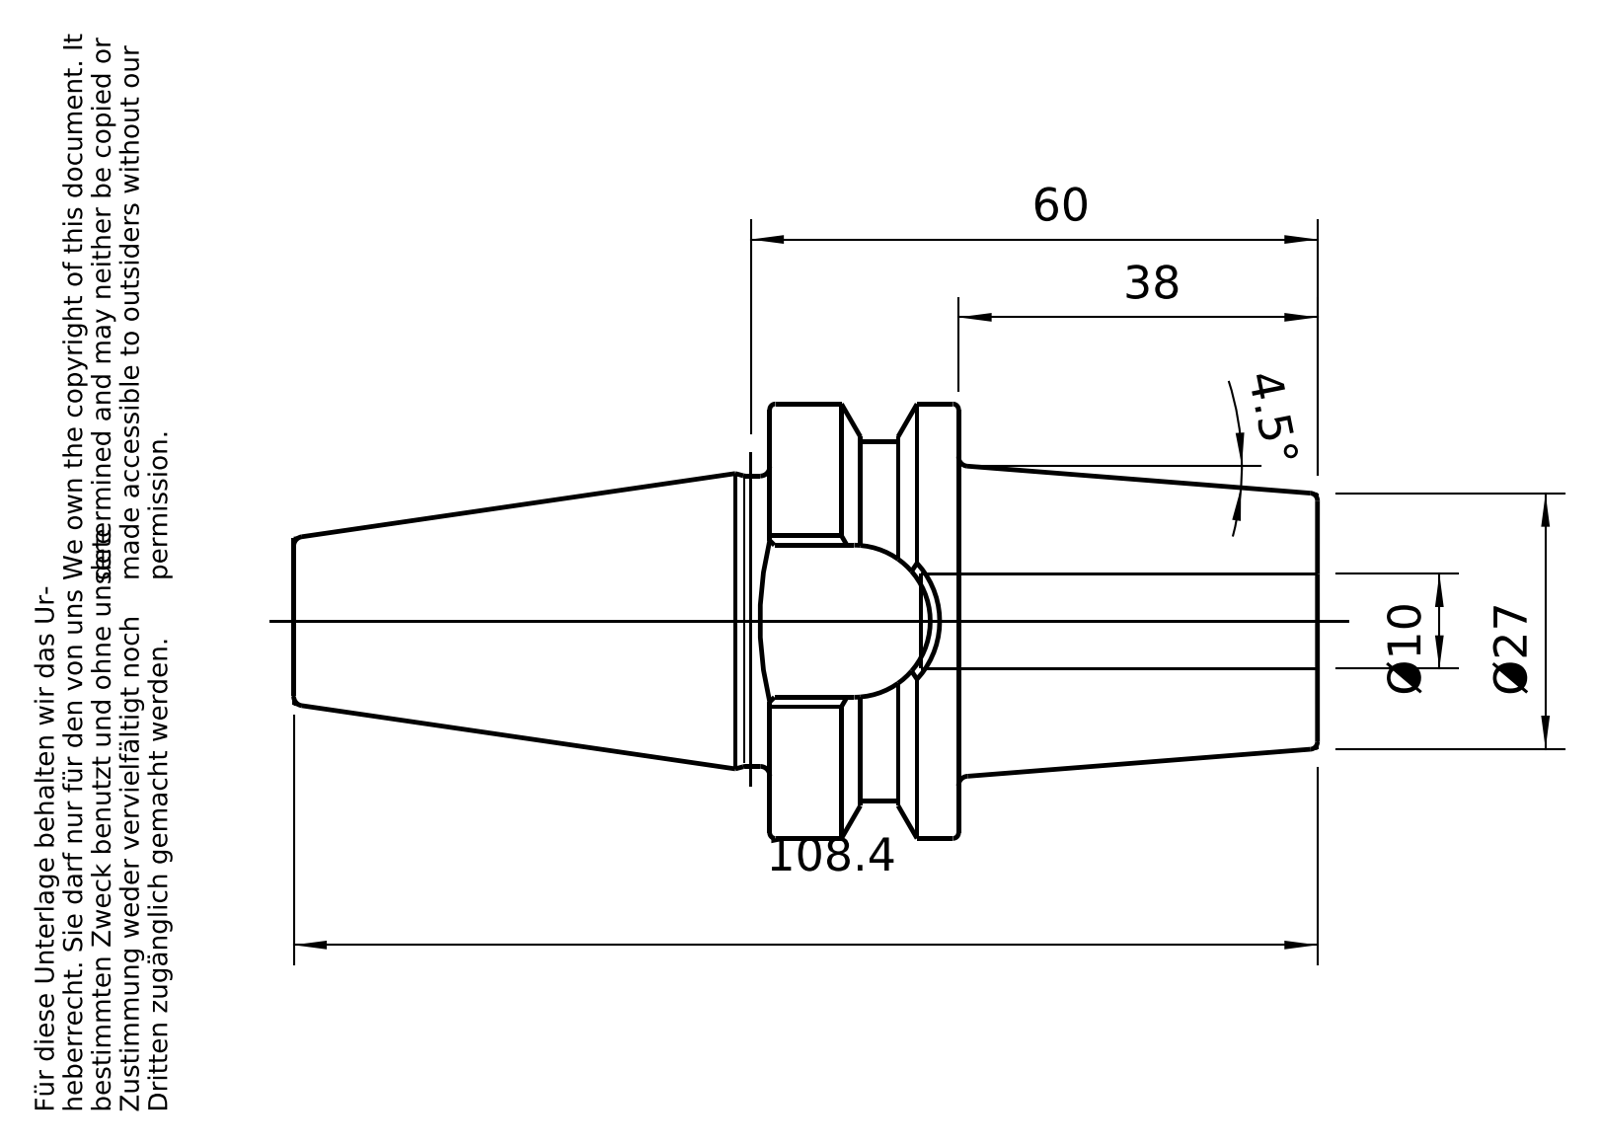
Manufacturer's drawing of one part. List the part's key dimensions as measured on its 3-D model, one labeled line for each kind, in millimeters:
Part name (STEP PRODUCT): 30-645-10
STEP written by: PRO/ENGINEER BY PARAMETRIC TECHNOLOGY CORPORATION, 2010430 (CONFIG_CONTROL_DESIGN)
Units: millimetres
Bodies: 1 solid, 94 faces (26 planar, 20 cylindrical, 48 other)
Overall size (bounding box): 108.4 × 45.98 × 45.98
Volume: 73 160 mm³ · Surface area: 16 406 mm²
Round holes (diameter × count): ⌀10 ×1, ⌀10.11 ×1, ⌀12.51 ×1, ⌀13 ×1
Round bosses / shafts (diameter × count): ⌀45.98 ×1, ⌀30.75 ×1, ⌀12.01 ×1
Partial cylindrical surfaces — rounded edges, fillets, slot ends (radius × count): R8.1 ×1, R18.88 ×1
Main face-to-face distances: 20, 58, 38, 32.3, 16, 4, 42, 16.2, 50.4, 66.4
